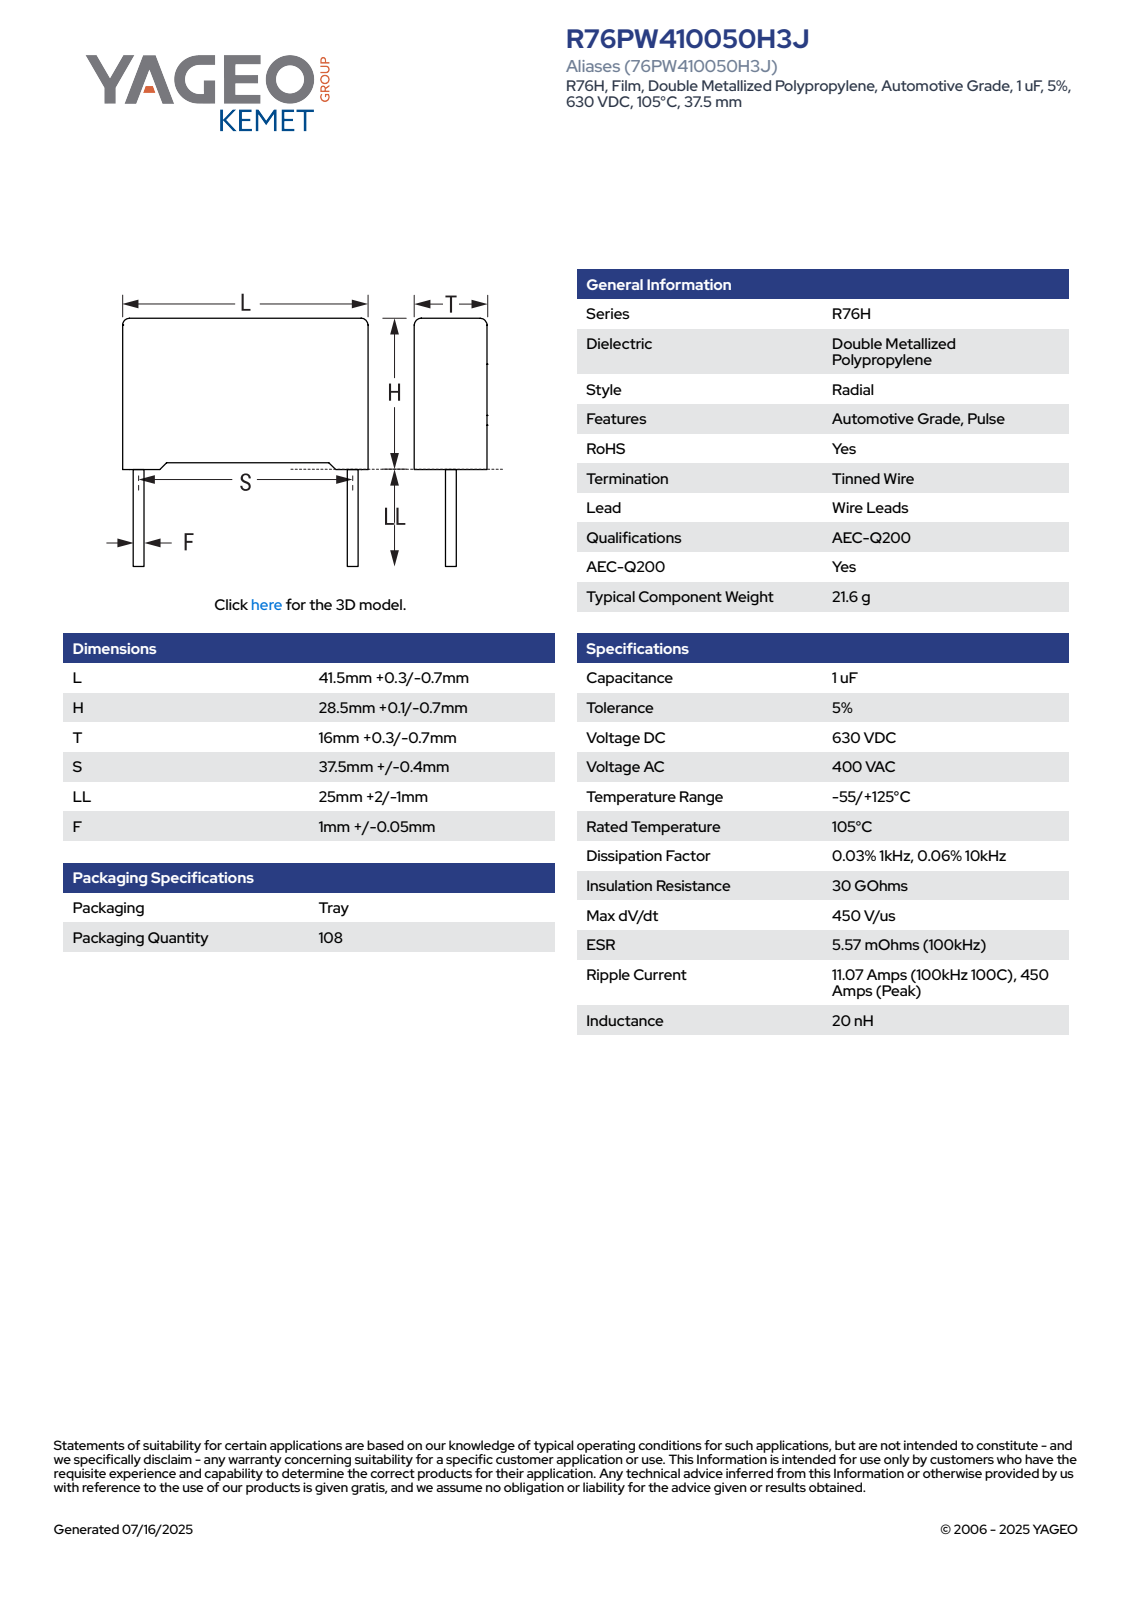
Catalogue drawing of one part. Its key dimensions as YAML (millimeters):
part_name: "CFR_RB2R76_41.5X28.5X16_L41.8H28.6T16.3S37.5LL27F1.05"
step_written_by: "SolidWorks 2014 (AUTOMOTIVE_DESIGN)"
units: millimeters
bodies: {solids: 4, faces: 85, planar: 77, cylindrical: 8, other: 0}
overall_size: [55.6, 41.8, 16.3]
volume: 18938
surface_area: 4942
round_bosses_or_shafts:
  - {diameter: 1.05, count: 2}
partial_cylinders:
  - {radius: 0.5, count: 4}
face_to_face_distances: [16.3, 27.61, 41.8, 27.85, 0.75, 0.99, 28.6, 16.31, 1.39, 40.41]
